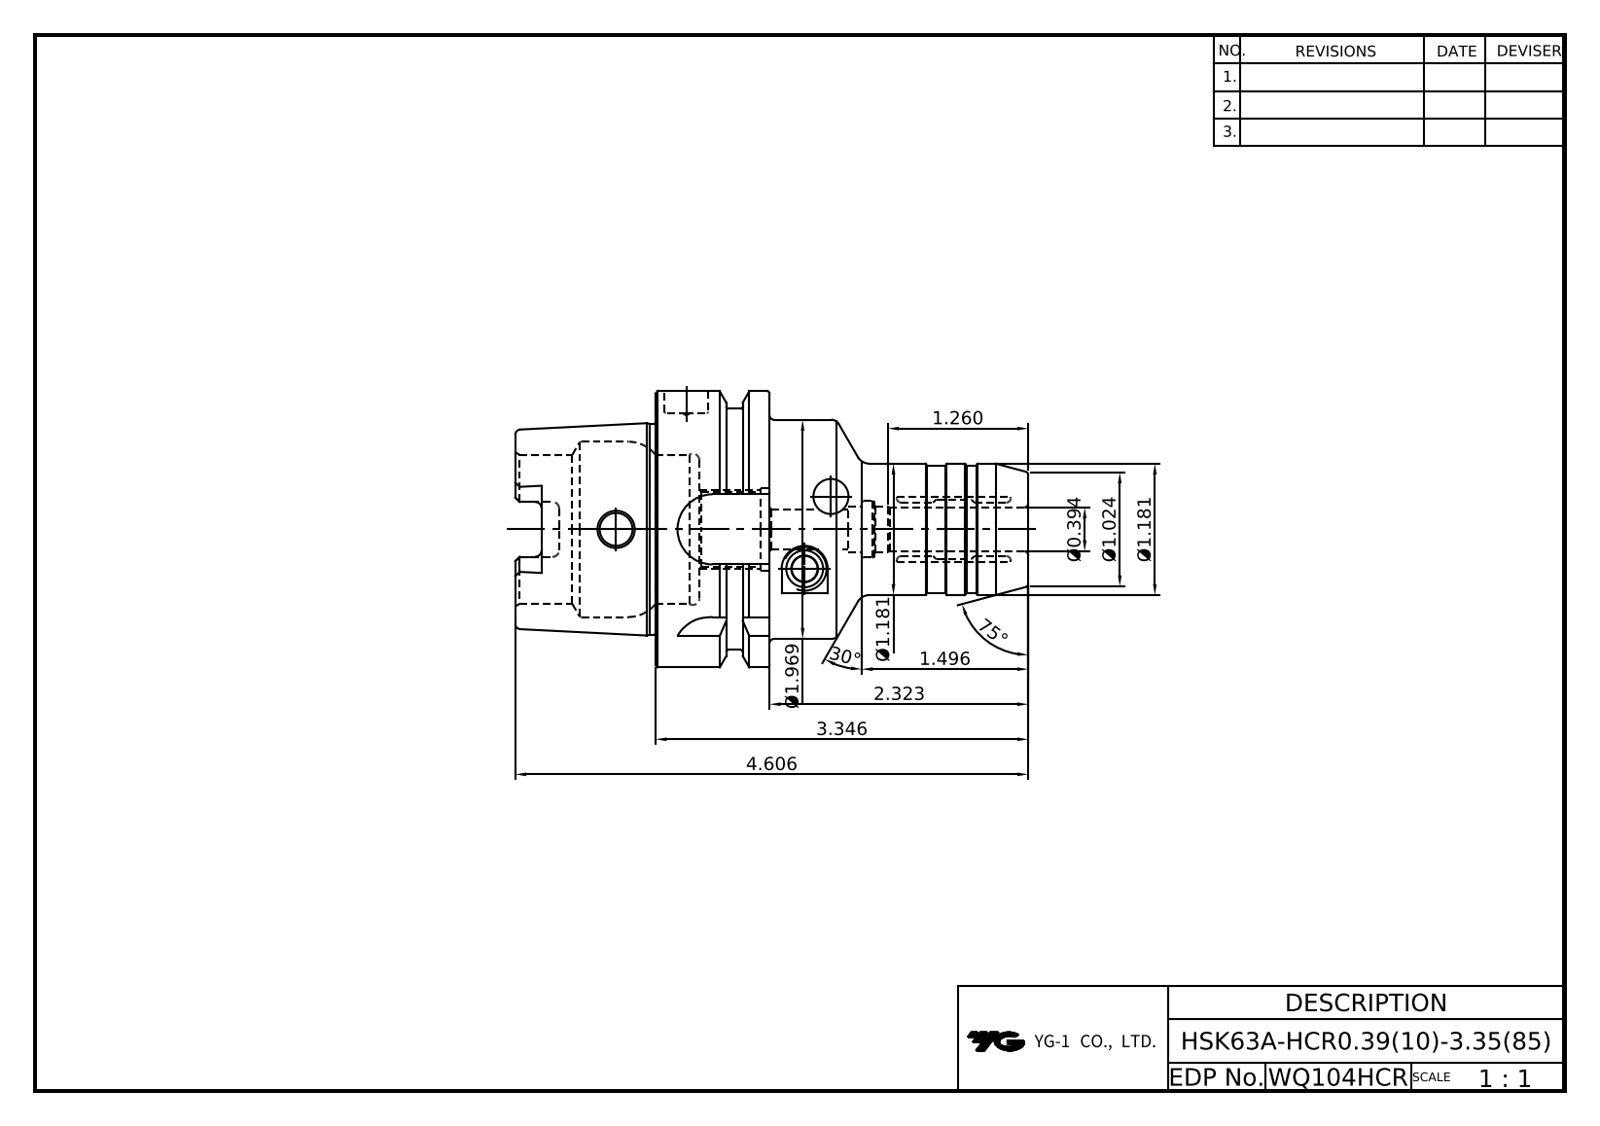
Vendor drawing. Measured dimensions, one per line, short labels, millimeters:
name: LO-HSK63A-HCR10-85
written by: Autodesk Inventor 2020 (AUTOMOTIVE_DESIGN)
unit: mm
bodies: 1 solid, 136 faces (42 planar, 38 cylindrical, 56 other)
size: 117 × 63 × 63
volume: 139 627 mm³; area: 30 076 mm²
holes: 2× ⌀10, 1× ⌀7.5, 1× ⌀9.2, 1× ⌀10.6, 1× ⌀16.92, 1× ⌀19, 1× ⌀34, 1× ⌀40
bosses: 1× ⌀63, 1× ⌀55, 1× ⌀50, 1× ⌀48.04, 1× ⌀30, 1× ⌀29
rounds: 6× R1.5, 4× R2.88, 4× R8
face distances: 26, 10, 16, 32, 59, 85, 75, 42, 58, 117
